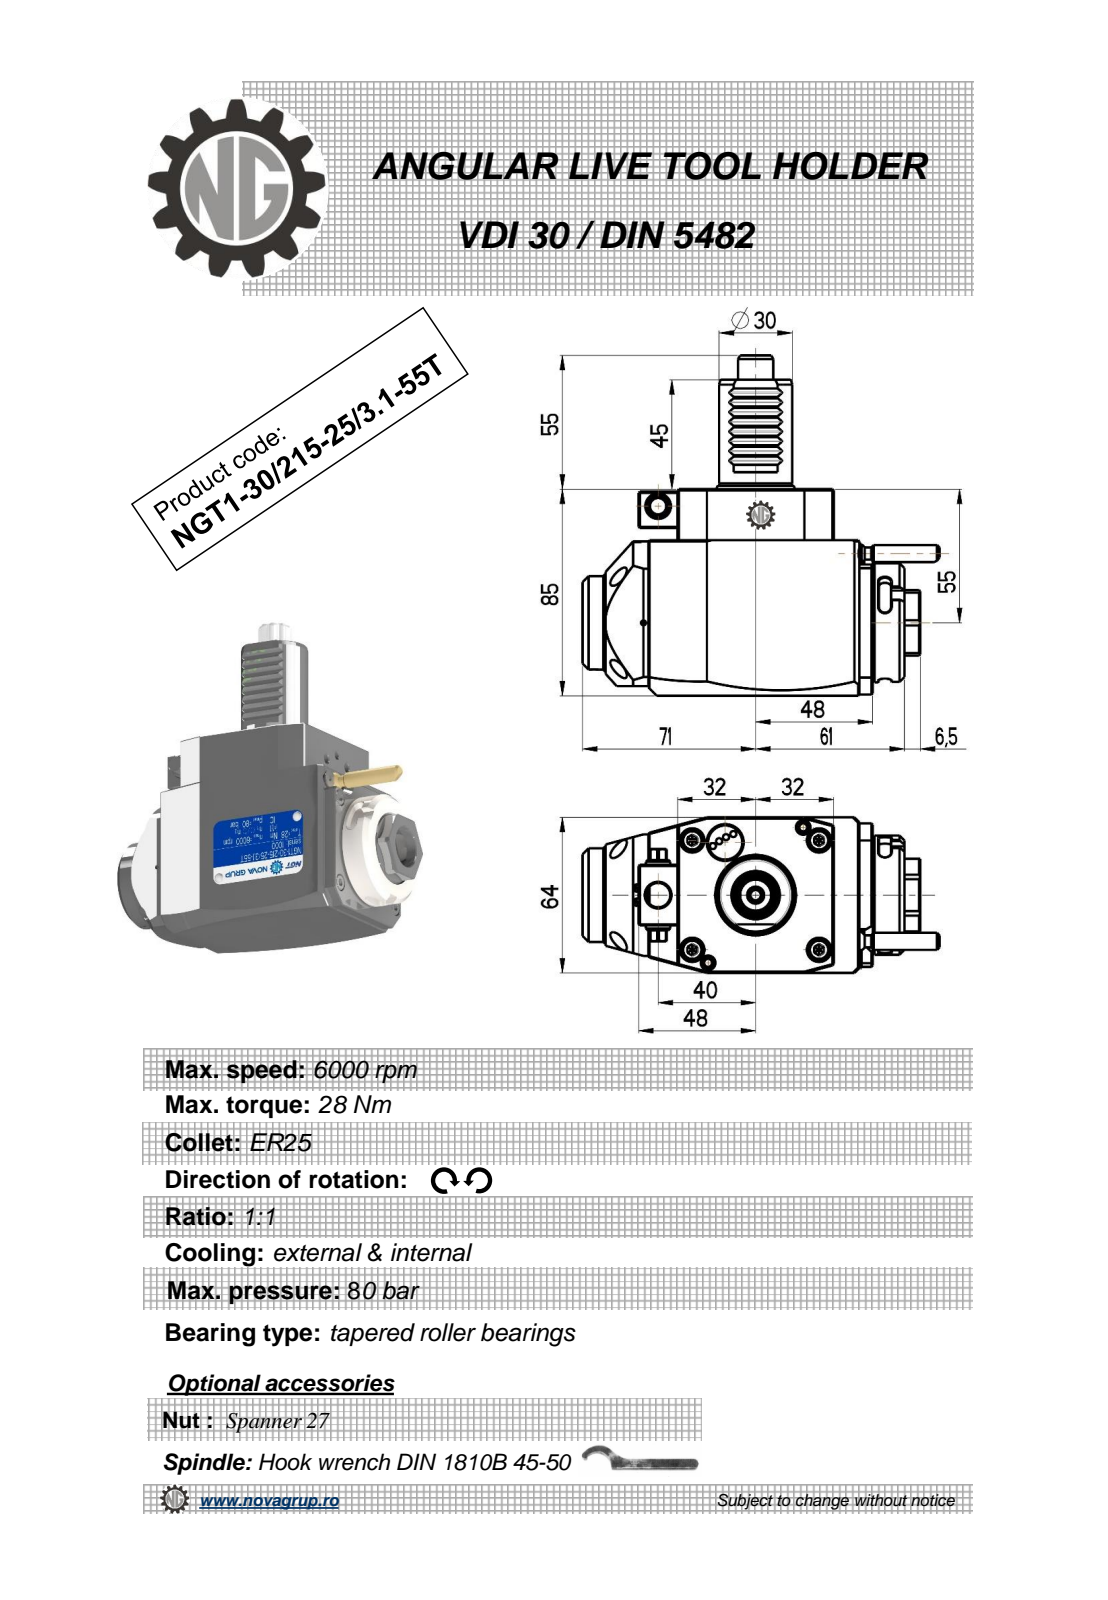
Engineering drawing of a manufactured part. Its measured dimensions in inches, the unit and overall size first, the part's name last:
Units: inches
Overall size (bounding box): 5.763 × 5.512 × 2.52
Round holes (diameter × count): ⌀0.098 ×1, ⌀0.118 ×1, ⌀0.165 ×1, ⌀0.209 ×1, ⌀0.335 ×1, ⌀0.374 ×1, ⌀0.394 ×1, ⌀0.709 ×1
Round bosses / shafts (diameter × count): ⌀0.315 ×2, ⌀1.929 ×1, ⌀1.654 ×1, ⌀1.516 ×1, ⌀1.181 ×1, ⌀0.394 ×1, ⌀0.276 ×1, ⌀0.197 ×1
Partial cylindrical surfaces — rounded edges, fillets, slot ends (radius × count): R0.115 ×16, R0.012 ×8, R0.098 ×6, R7.087 ×2, R0.152 ×1, R0.177 ×1, R0.226 ×1, R0.285 ×1
Main face-to-face distances: 2.52, 3.346, 0.63, 3.15, 0.512, 0.827, 1.142, 4.055, 4.685, 5.197
Hole centre spacings: 1.03, 1.348, 1.575, 1.831
Volume: 34.1 in³ · Surface area: 77.52 in²
Bodies: 1 solid, 378 faces (176 planar, 114 cylindrical, 88 other)
Part name (STEP PRODUCT): NGT1_30_215_25_3_1_55T
STEP written by: PRO/ENGINEER BY PARAMETRIC TECHNOLOGY CORPORATION, 2010280 (CONFIG_CONTROL_DESIGN)
